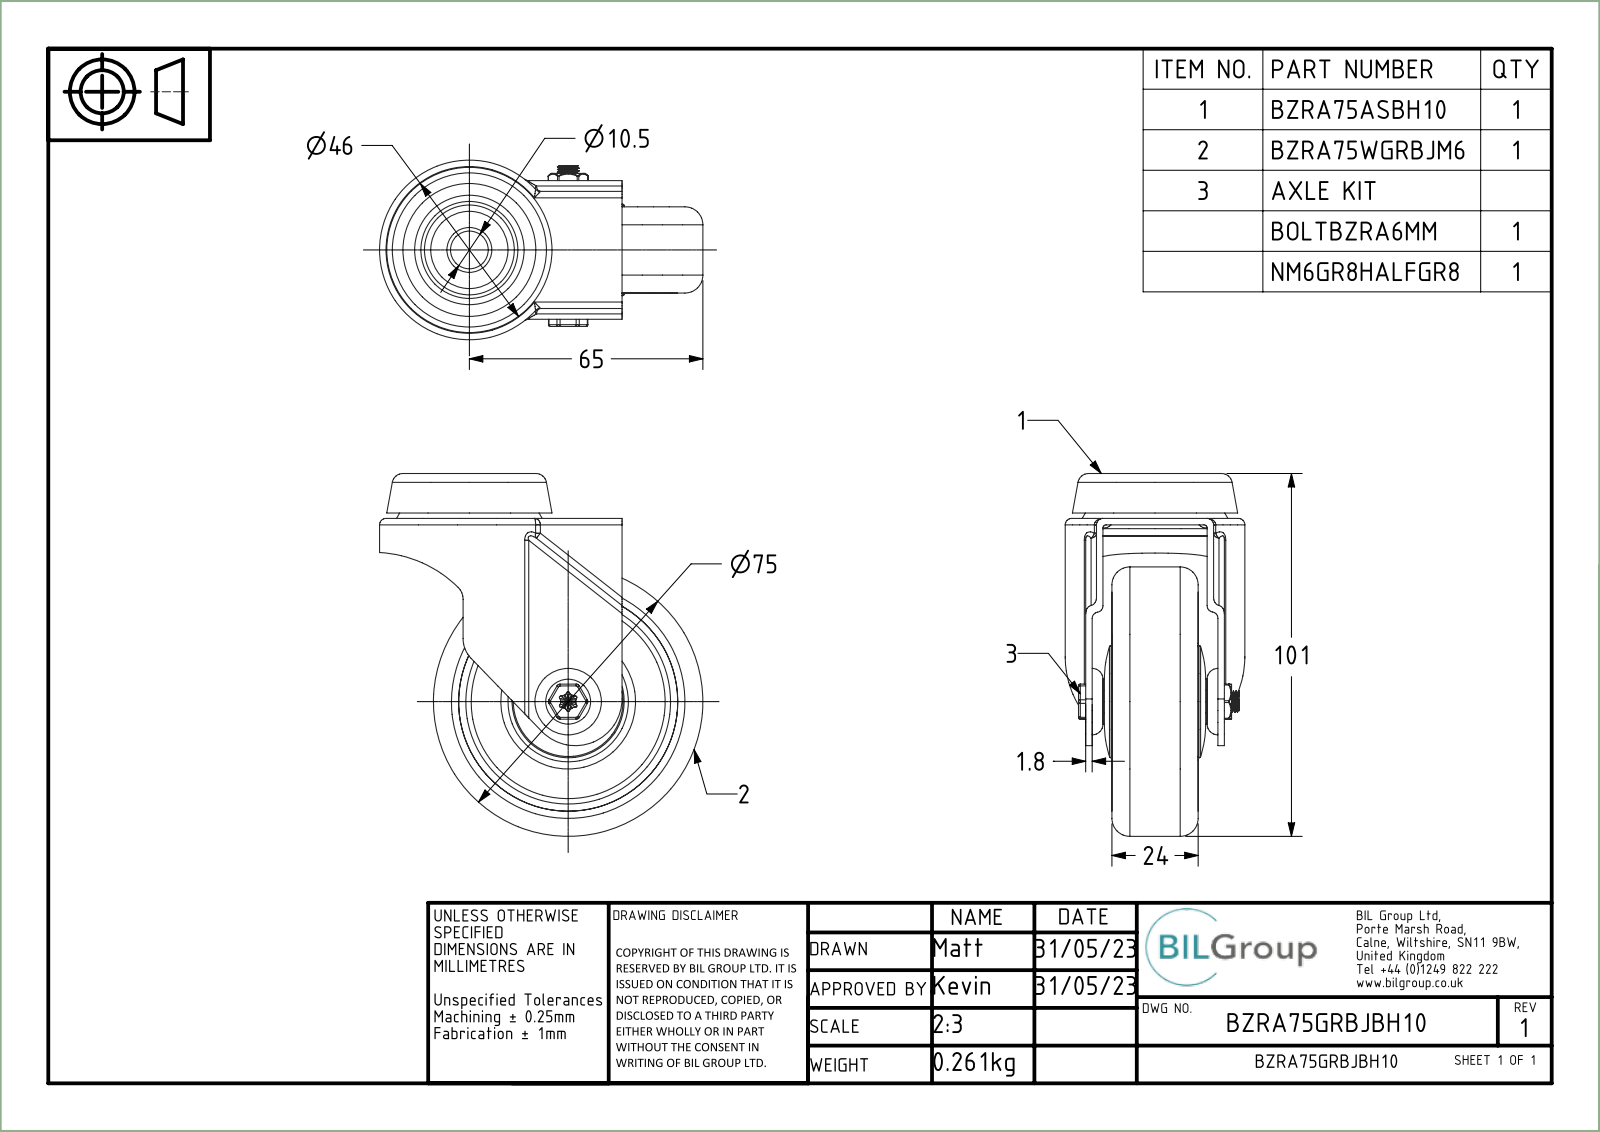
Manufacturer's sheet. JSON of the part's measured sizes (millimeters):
{"part_name": "BZRA75ASBH10; ZINC PLATED PRESSED STEEL FORKS; ZINC PLATED PRESSED STEEL HEAD; BZRA75GRBJBH10 (+8 more)", "step_written_by": "Spatial InterOp 3D (CONFIG_CONTROL_DESIGN)", "units": "millimeters", "bodies": {"solids": 19, "faces": 594, "planar": 98, "cylindrical": 253, "other": 243}, "overall_size": [101, 90, 50], "volume_mm3": 88867, "surface_area_mm2": 67974, "round_holes": [[6, 1], [6.1, 1], [6.5, 1], [6.8, 1], [8, 1], [8.5, 1], [10.5, 1], [10.55, 1], [11.2, 1], [12.74, 1], [18, 1], [18.3, 1]], "round_bosses_or_shafts": [[75, 1], [37.5, 1], [31.25, 1], [28, 1], [22, 1], [18.7, 1], [18.32, 1], [12.5, 1]], "partial_cylinders_radius": [[1, 18], [1.8, 14], [0.5, 12], [0.4, 6], [0.9, 6], [2.12, 1], [4.63, 1], [8, 1]], "face_to_face_distances": [11, 1.8, 33.8, 15.5, 13, 3, 7.3, 18.3, 20.3, 31.3]}
